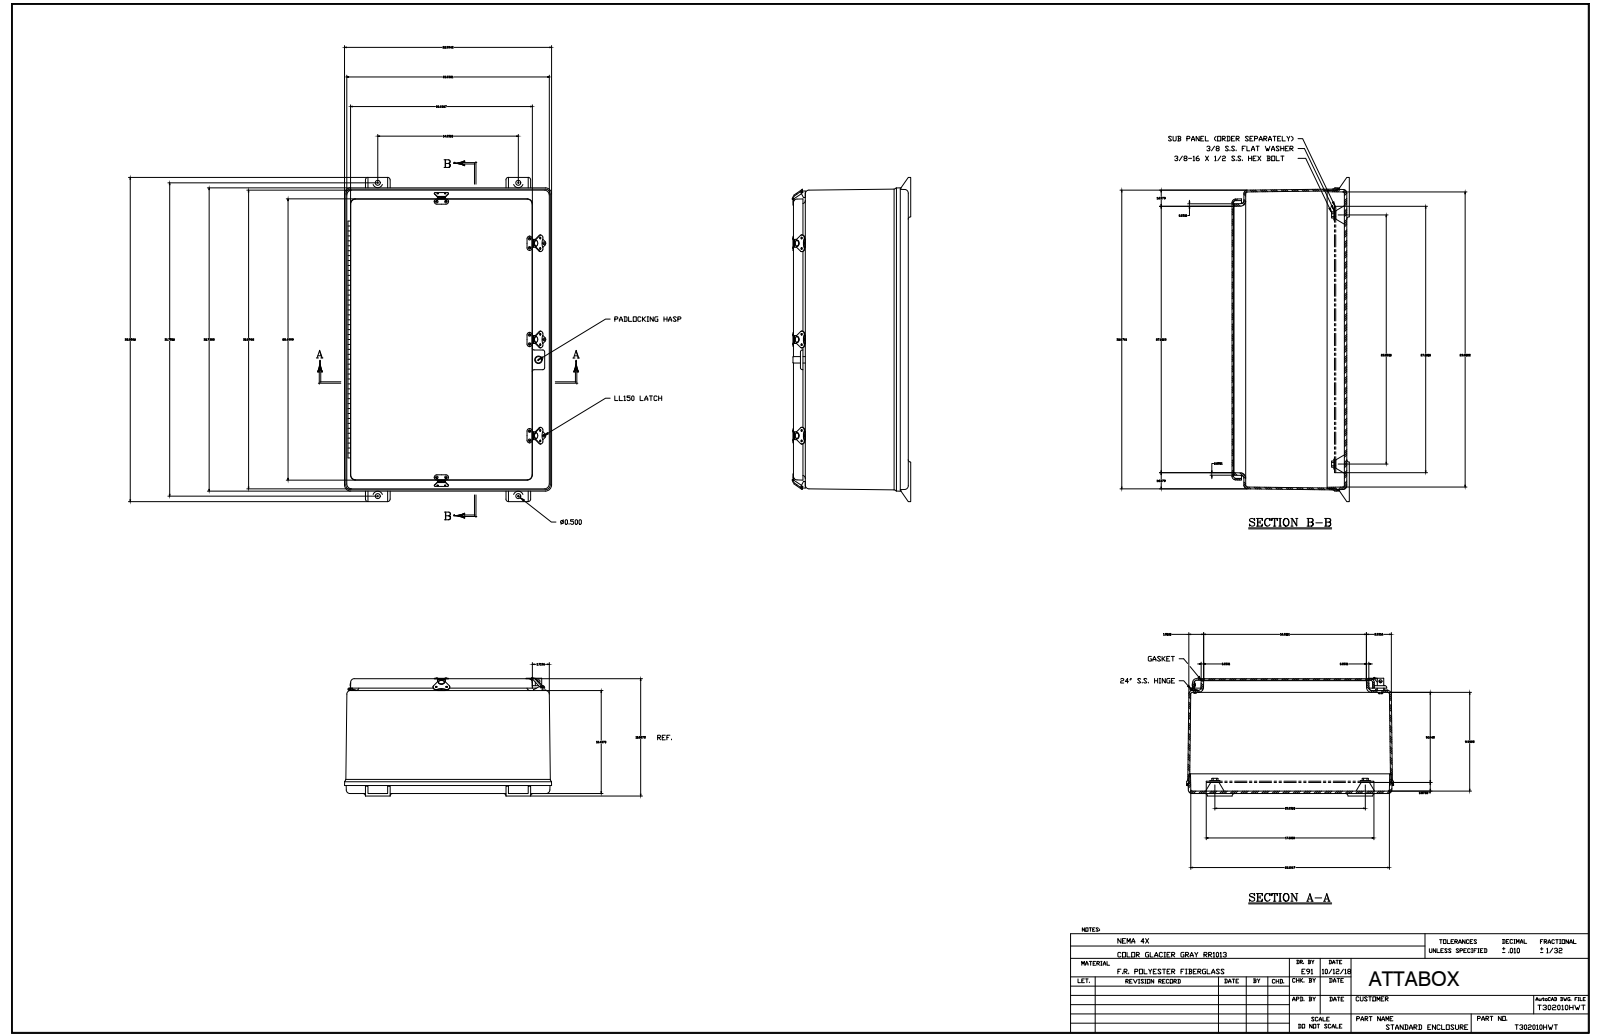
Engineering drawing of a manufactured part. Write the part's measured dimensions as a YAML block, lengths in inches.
part_name: "T302010HWT"
step_written_by: "SolidWorks 2018 (AUTOMOTIVE_DESIGN)"
units: inches
bodies: {solids: 63, faces: 1747, planar: 659, cylindrical: 702, other: 386}
overall_size: [32.844, 21, 12.241]
volume: 520.5
surface_area: 5525
round_holes:
  - {diameter: 0.13, count: 36}
  - {diameter: 0.063, count: 20}
  - {diameter: 0.138, count: 10}
  - {diameter: 0.187, count: 10}
  - {diameter: 0.065, count: 5}
  - {diameter: 0.563, count: 4}
  - {diameter: 0.065, count: 3}
  - {diameter: 0.135, count: 3}
  - {diameter: 0.156, count: 3}
  - {diameter: 0.51, count: 2}
  - {diameter: 0.51, count: 2}
  - {diameter: 0.125, count: 1}
round_bosses_or_shafts:
  - {diameter: 0.14, count: 20}
  - {diameter: 0.297, count: 8}
  - {diameter: 0.5, count: 5}
  - {diameter: 0.2, count: 3}
  - {diameter: 0.135, count: 3}
  - {diameter: 0.25, count: 1}
  - {diameter: 0.201, count: 1}
partial_cylinders:
  - {radius: 0.01, count: 127}
  - {radius: 0.25, count: 24}
  - {radius: 0.03, count: 20}
  - {radius: 0.187, count: 14}
  - {radius: 0.375, count: 13}
  - {radius: 0.312, count: 12}
  - {radius: 0.5, count: 12}
  - {radius: 0.313, count: 11}
face_to_face_distances: [0.187, 0.25, 11.5, 11.25, 0.156, 11.656, 11.406, 10.437, 10.25, 1.25]
hole_center_spacings: [9.75, 7.5, 15.5, 0.858, 1.542, 19.5, 1, 8]
